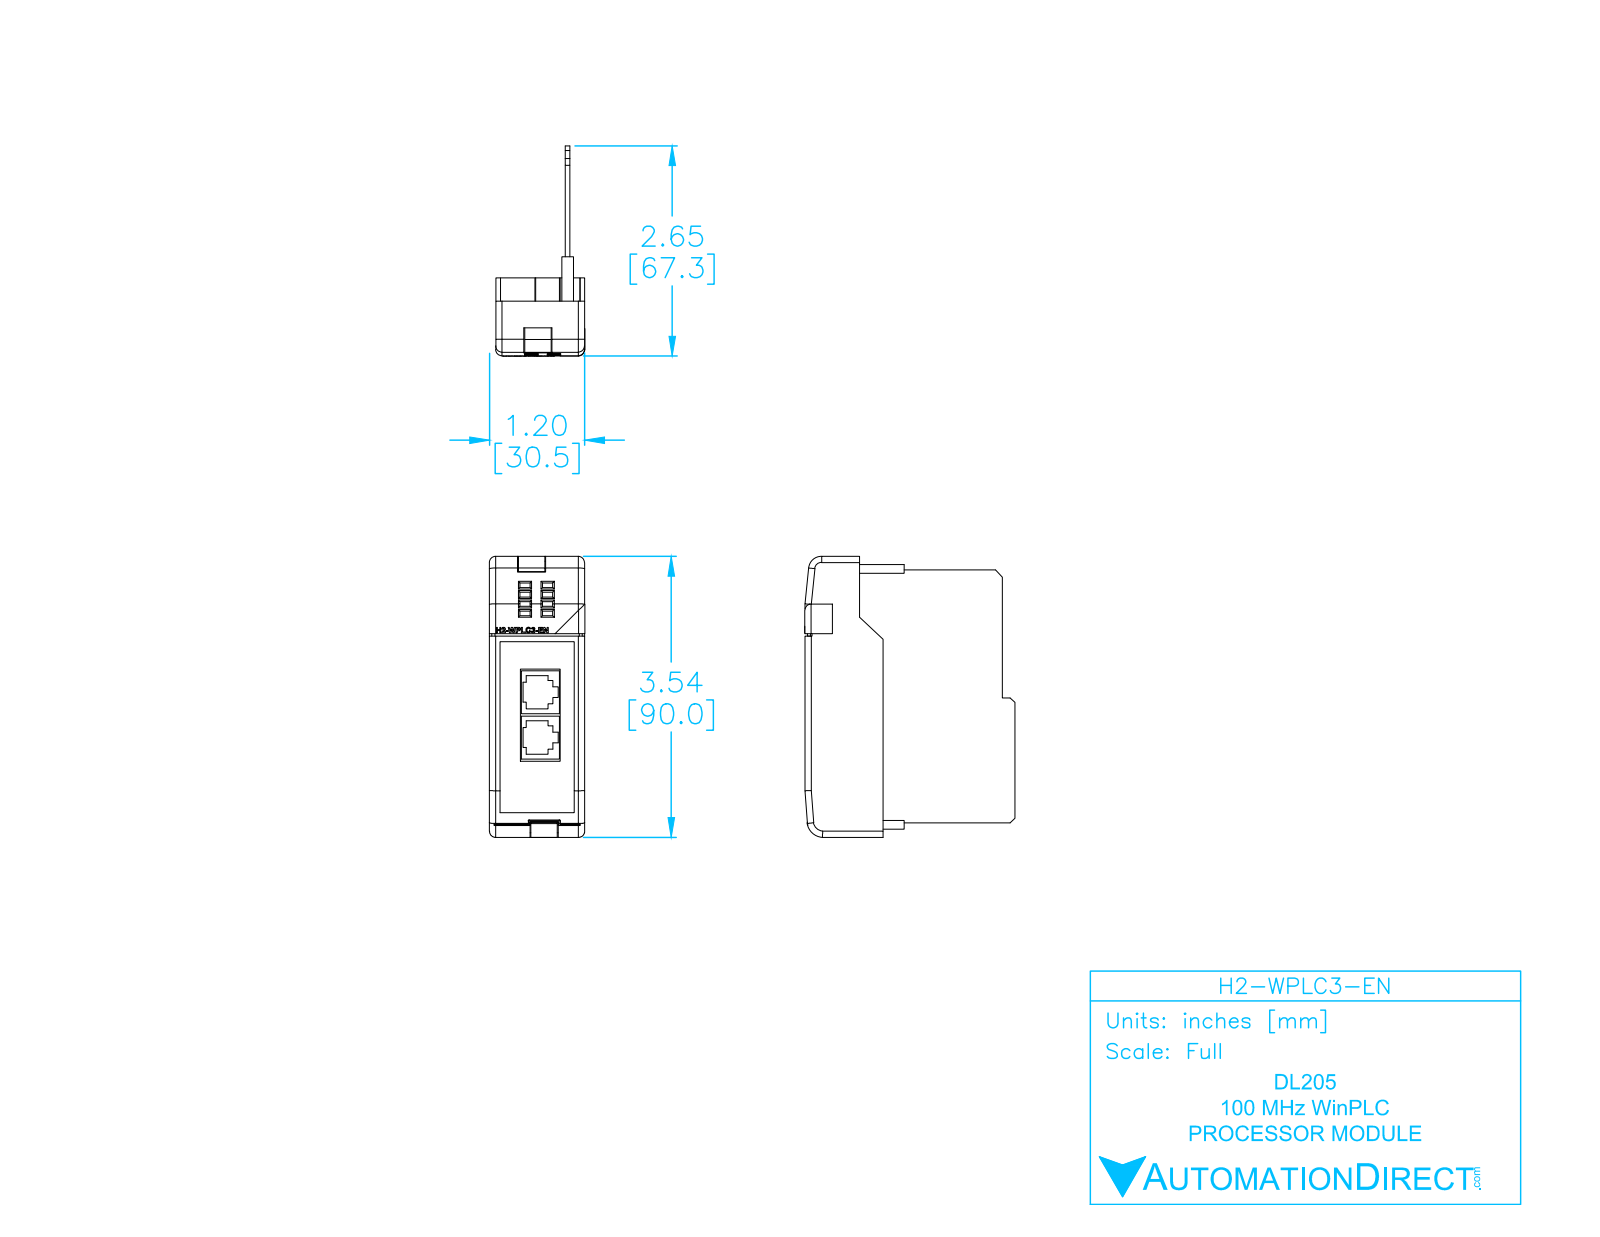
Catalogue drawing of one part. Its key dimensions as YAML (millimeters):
part_name: "H2-WPLC3-EN"
step_written_by: "SolidWorks 2009 (AUTOMOTIVE_DESIGN)"
units: millimeters
bodies: {solids: 4, faces: 441, planar: 309, cylindrical: 84, other: 48}
overall_size: [90, 67.38, 30.55]
volume: 19329
surface_area: 29786
partial_cylinders:
  - {radius: 0.5, count: 28}
  - {radius: 2, count: 11}
  - {radius: 0.25, count: 4}
  - {radius: 1, count: 2}
  - {radius: 2.62, count: 1}
  - {radius: 3.79, count: 1}
  - {radius: 4.12, count: 1}
  - {radius: 5.29, count: 1}
face_to_face_distances: [1.5, 4.72, 3.22, 6.22, 24.28, 29, 0.5, 25.78, 30.5, 22.78]
